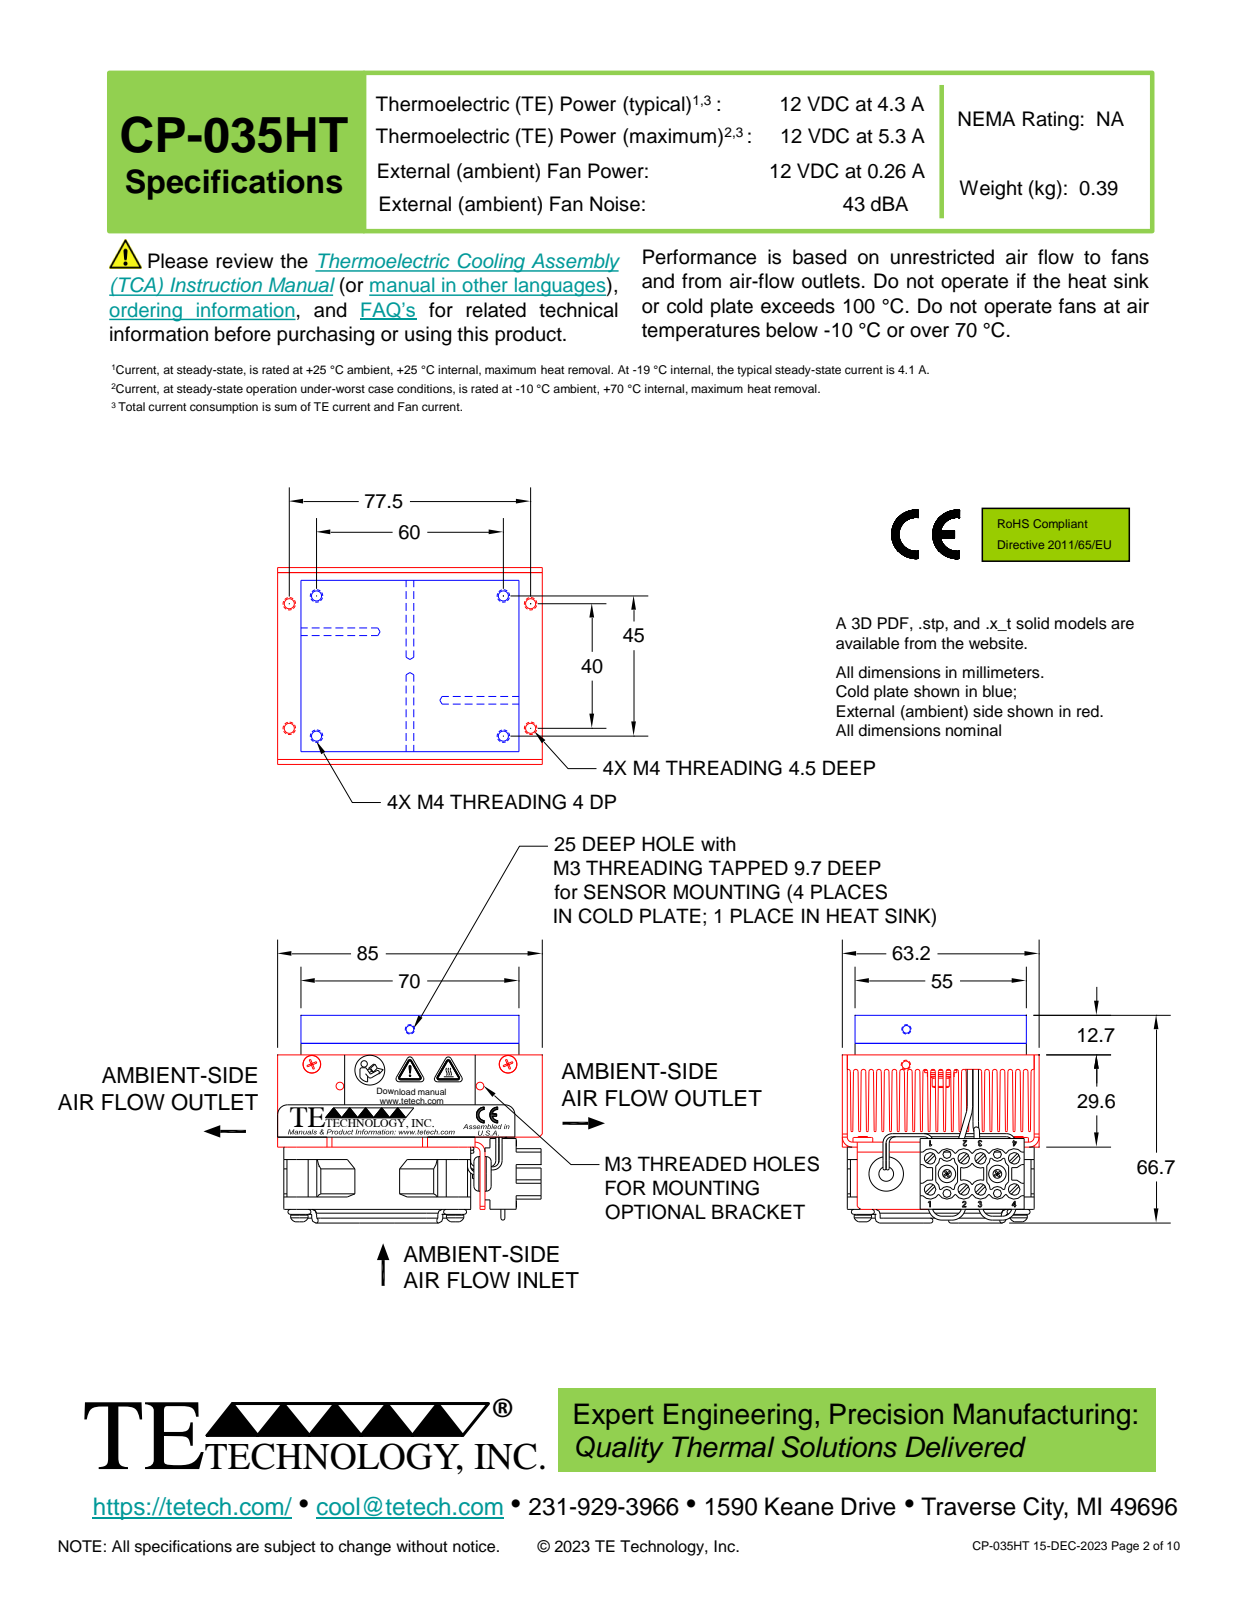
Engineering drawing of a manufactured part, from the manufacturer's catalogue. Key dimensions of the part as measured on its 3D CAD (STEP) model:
Part name (STEP PRODUCT): gasket CP-035HT; 810-7679-001 HEAT SINK SHROUD; PEM CLS-M3-2; 810-7679-001 with pems (+8 more)
STEP written by: Alibre (AUTOMOTIVE_DESIGN)
Units: millimetres
Bodies: 82 solids, 2349 faces (1175 planar, 350 cylindrical, 824 other)
Overall size (bounding box): 85 × 66.69 × 63.23
Volume: 161 925 mm³ · Surface area: 147 927 mm²
Round holes (diameter × count): ⌀2.46 ×10, ⌀3.24 ×8, ⌀2.46 ×6, ⌀4.22 ×6, ⌀4.5 ×5, ⌀3.5 ×2, ⌀3.56 ×2, ⌀3.8 ×2, ⌀4.17 ×2, ⌀4.22 ×2, ⌀6.4 ×2, ⌀11.1 ×2
Round bosses / shafts (diameter × count): ⌀0.99 ×14, ⌀1.59 ×11, ⌀6.35 ×6, ⌀5.59 ×6, ⌀5.28 ×6, ⌀4.2 ×6, ⌀3 ×6, ⌀1.78 ×6
Partial cylindrical surfaces — rounded edges, fillets, slot ends (radius × count): R0.5 ×21, R0.2 ×8, R0.4 ×8, R1 ×8, R4 ×8, R1.5 ×7, R6 ×7, R0.17 ×6
Main face-to-face distances: 3, 9, 6, 12, 1.2, 4.2, 1.8, 4.8, 7.2, 15
Hole centre spacings: 9.1, 21.45, 22.52, 35.36, 43.39, 50, 65.02, 68.8
